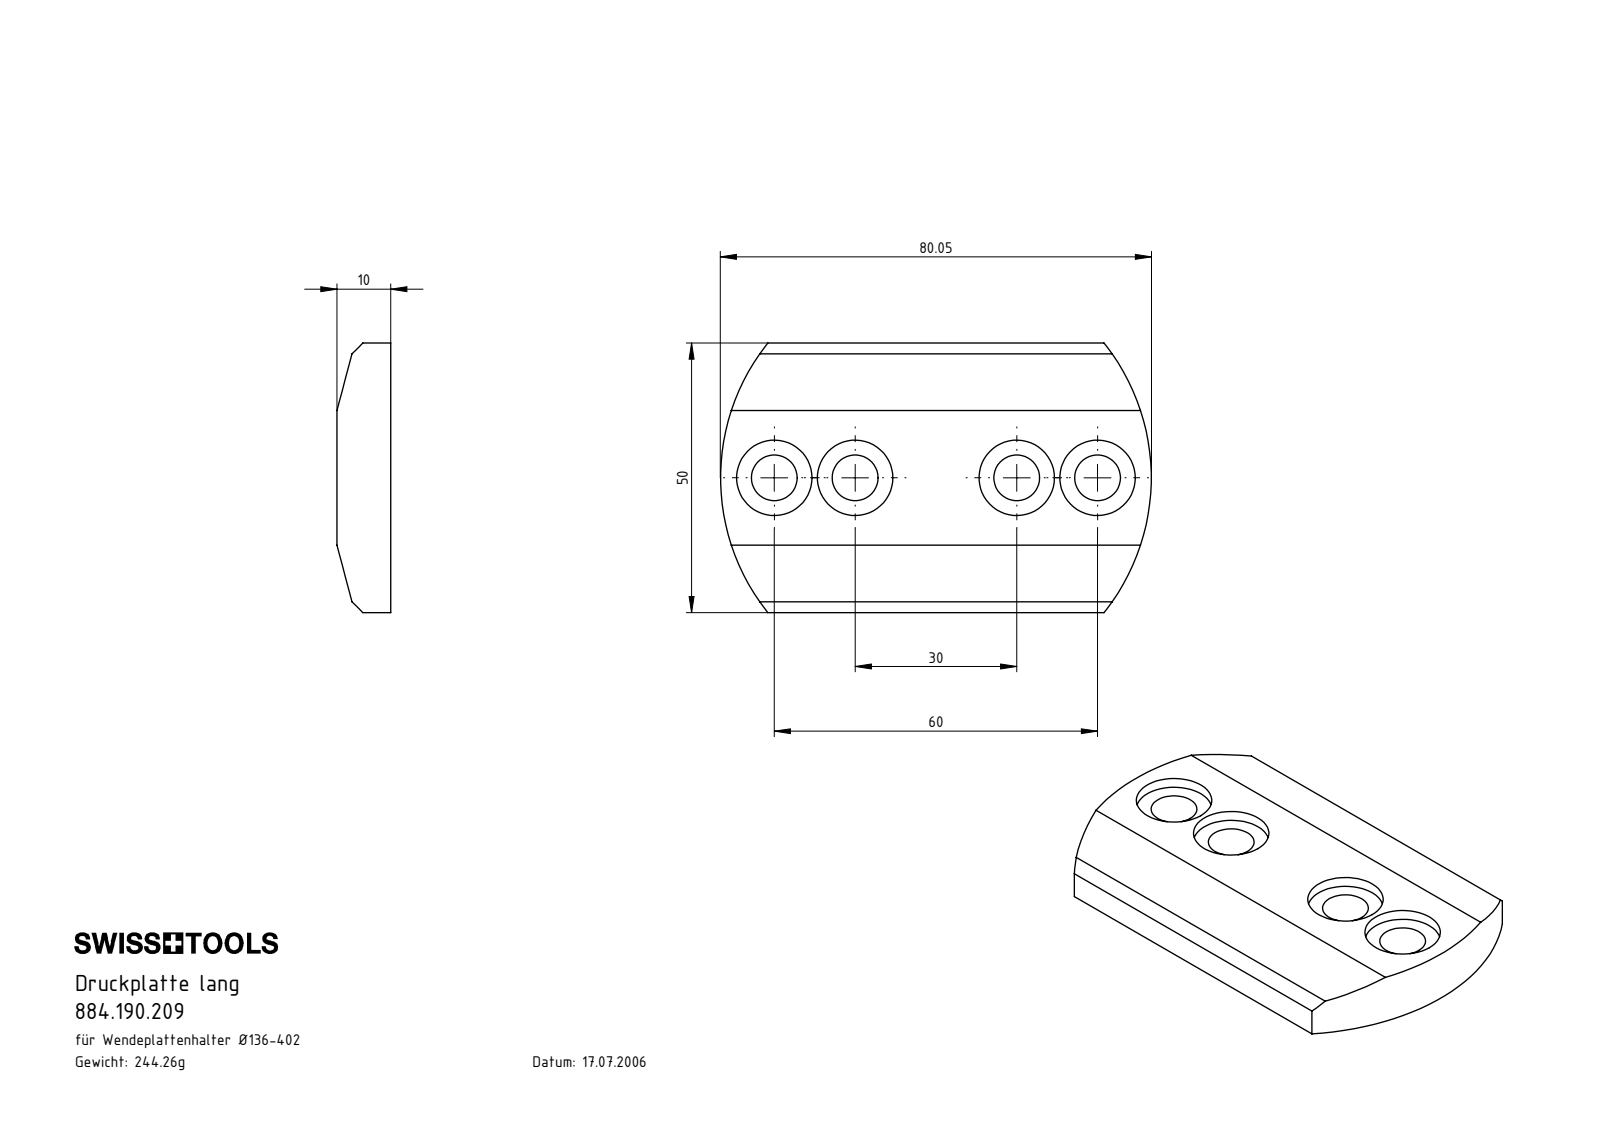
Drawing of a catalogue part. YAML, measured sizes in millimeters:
part_name: "884.190.209"
step_written_by: "SolidWorks 2022 (CONFIG_CONTROL_DESIGN)"
units: millimeters
bodies: {solids: 1, faces: 30, planar: 12, cylindrical: 18, other: 0}
overall_size: [79.95, 50, 10]
volume: 31116
surface_area: 9971
round_holes:
  - {diameter: 8.5, count: 4}
  - {diameter: 14, count: 4}
partial_cylinders:
  - {radius: 40, count: 2}
face_to_face_distances: [10, 8, 2, 50]
hole_center_spacings: [15, 45, 30, 60]
